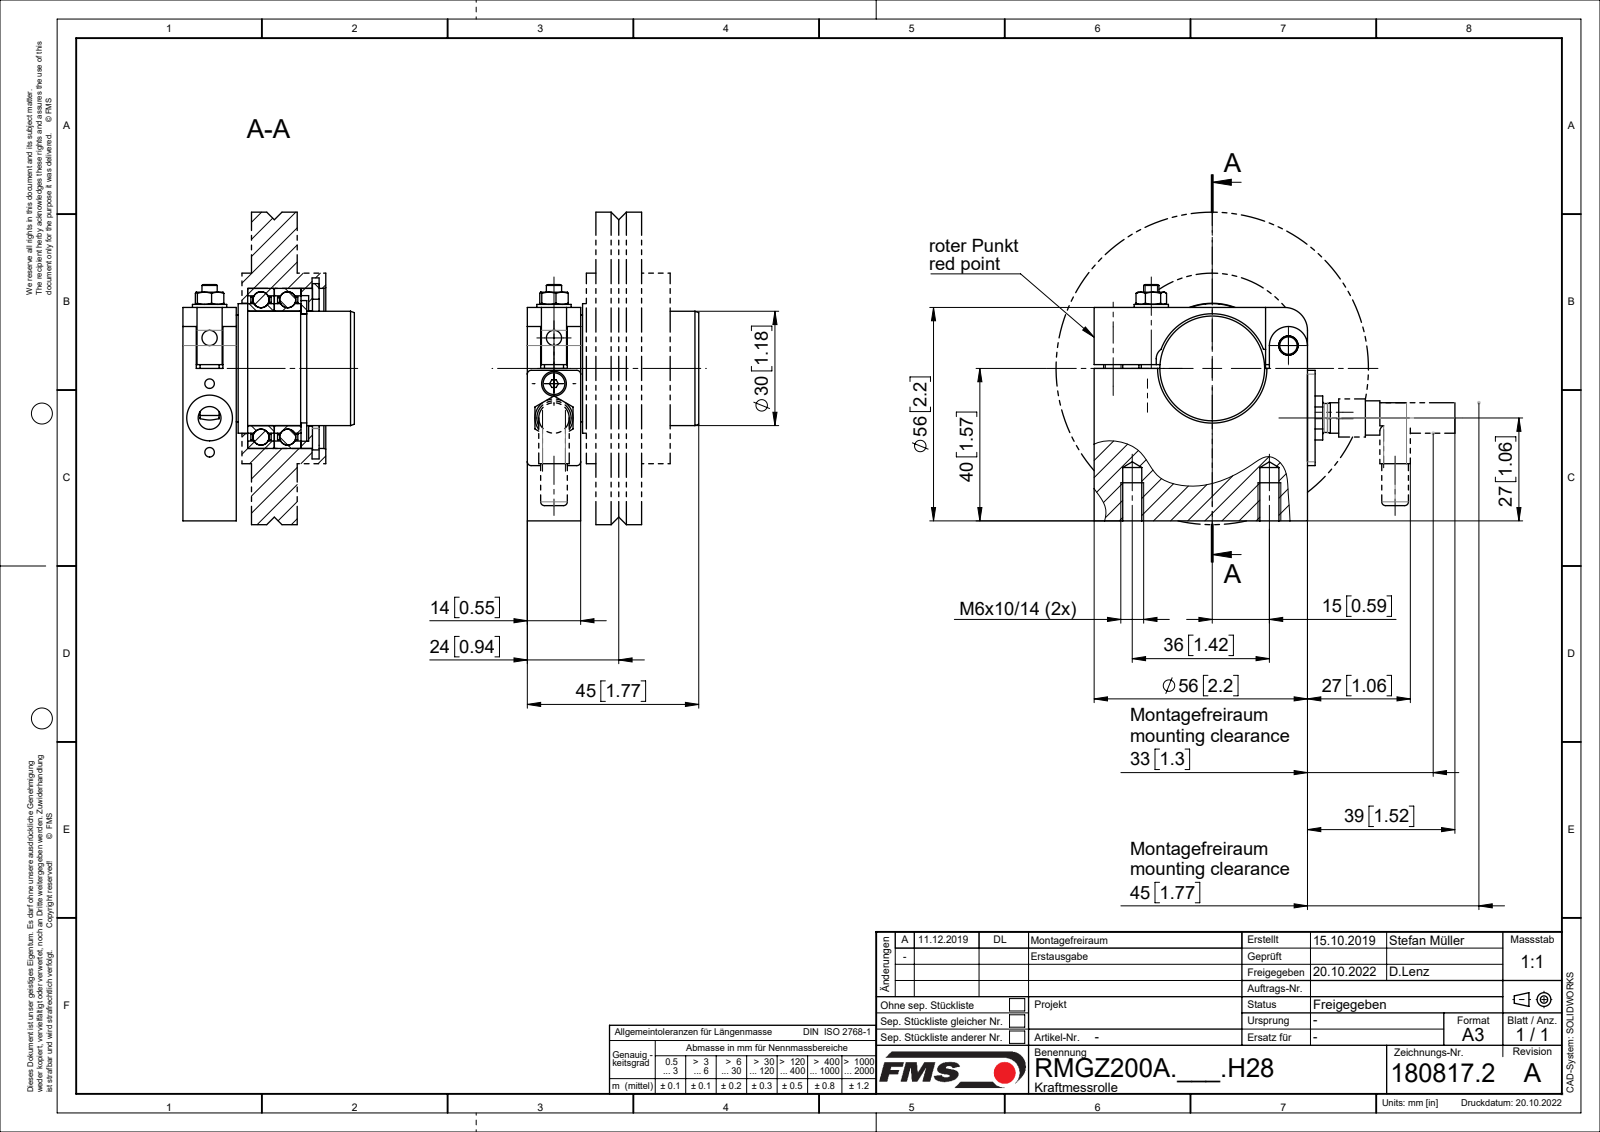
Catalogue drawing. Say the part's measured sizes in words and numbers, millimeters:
The part is named "R1609051_STANDARD; R1609053; R1609054; R1609052 (+8 more)". Its 3-D file was written by "Mechanical Desktop 2009 (CONFIG_CONTROL_DESIGN)". It is 21 solids with 470 faces: 153 planar, 198 cylindrical and 119 other. Overall it measures 66.5 by 62.25 by 45 millimeters. Its volume is 70 725 cubic millimeters and its surface area 40 280 square millimeters. Round holes: 7 of diameter 3.2, 6 of diameter 2.6, 4 of diameter 6.4, 3 of diameter 4, 2 of diameter 2.2, 2 of diameter 5.15, 2 of diameter 6, 1 of diameter 3.42, 1 of diameter 3.5, 1 of diameter 4.3, 1 of diameter 4.33, 1 of diameter 5. Round bosses or shafts: 6 of diameter 3, 4 of diameter 5.5, 4 of diameter 1, 2 of diameter 8, 2 of diameter 6, 1 of diameter 44.5, 1 of diameter 42, 1 of diameter 36.4. Partial cylindrical surfaces (rounded edges, fillets, slot ends): 4 of radius 1, 1 of radius 2.5, 1 of radius 3, 1 of radius 4.1, 1 of radius 5, 1 of radius 6. The main face-to-face distances are 14, 10, 17, 7, 3, 20, 31, 34, 16, 9. The hole center spacings are 9, 18, 9.85, 10.3, 15.81, 5, 8, 4.
